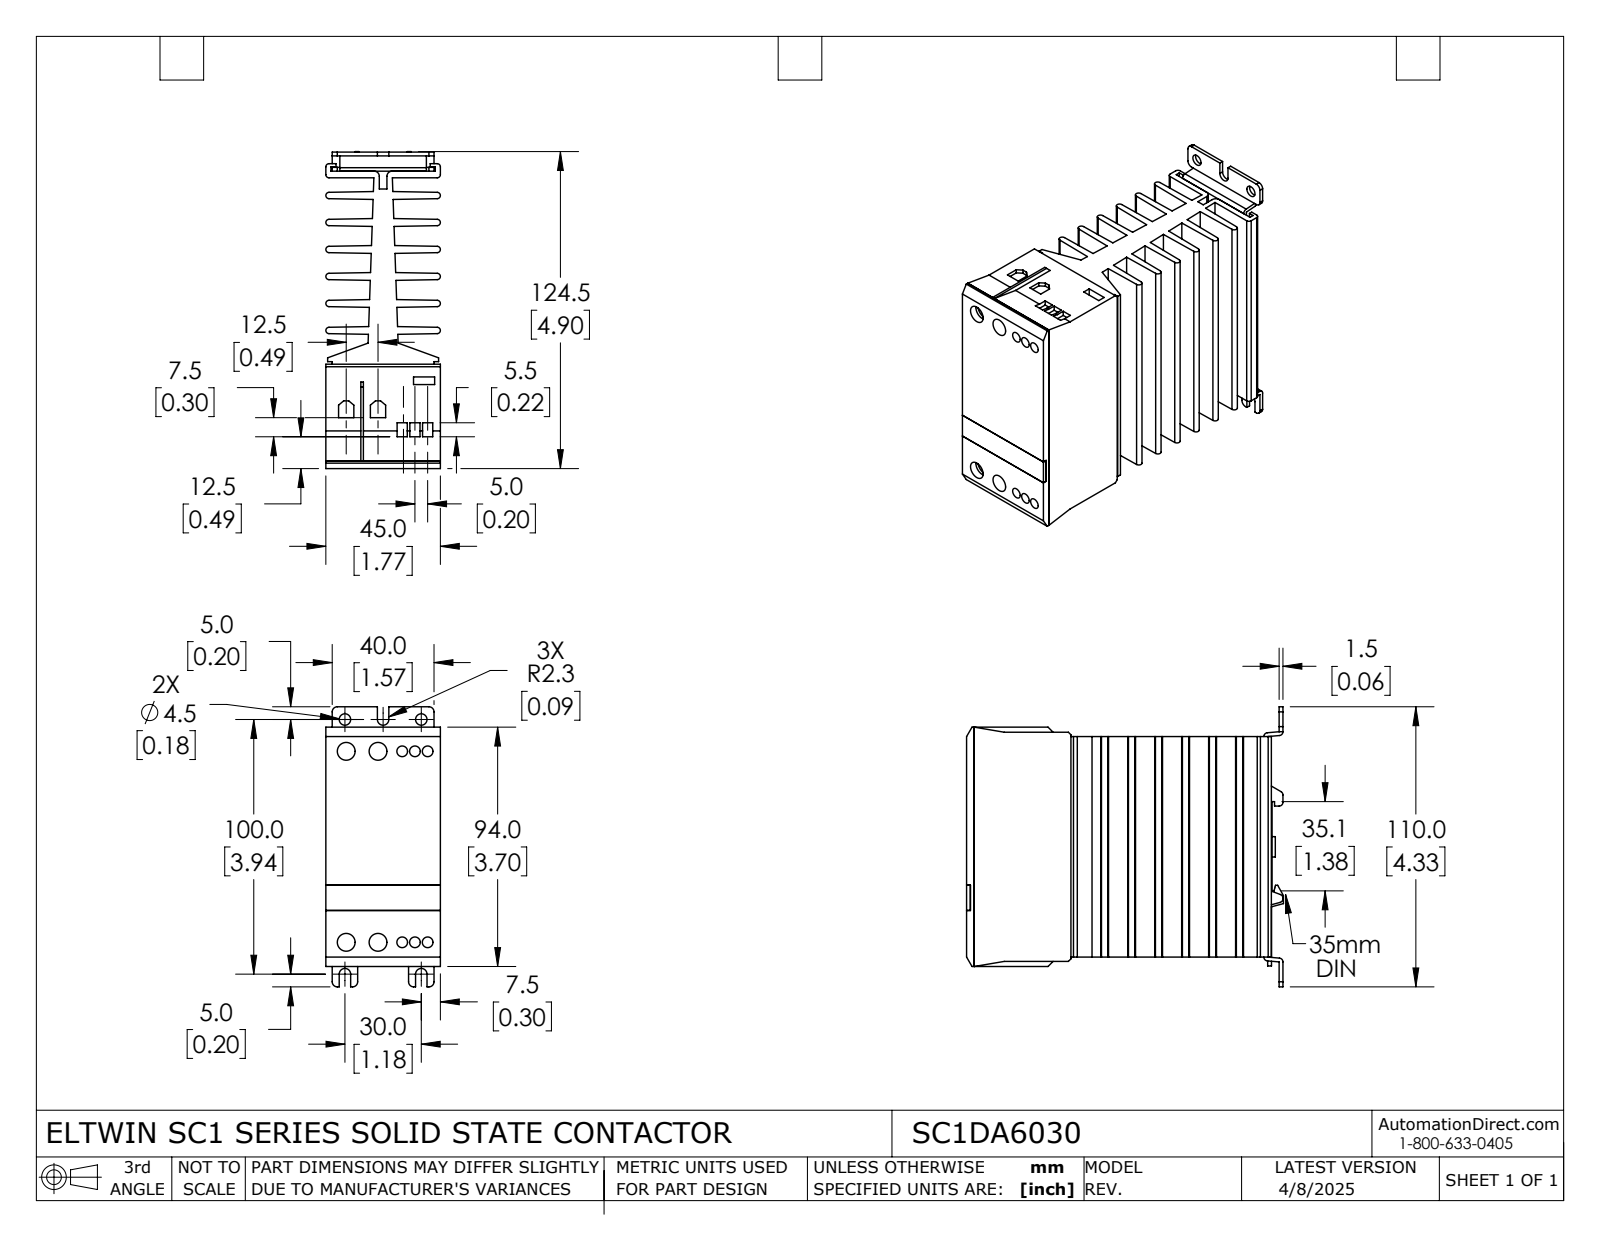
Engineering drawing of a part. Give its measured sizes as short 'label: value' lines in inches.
name: SC1DA6030
written by: SolidWorks 2021 (AUTOMOTIVE_DESIGN)
unit: in
bodies: 7 solids, 391 faces (284 planar, 107 cylindrical, 0 other)
size: 4.902 × 4.331 × 1.772
volume: 18.87 in³; area: 165.4 in²
holes: 6× ⌀0.165, 6× ⌀0.173, 4× ⌀0.276, 2× ⌀0.177, 2× ⌀0.315
bosses: 3× ⌀0.315
rounds: 18× R0.079, 16× R0.049, 10× R0.059, 4× R0.051, 3× R0.089
face distances: 0.417, 0.835, 0.127, 1.252, 0.29, 0.544, 0.707, 0.962, 1.669, 1.125
hole spacings: 2.953, 0.197, 2.959, 0.374, 0.394, 0.492, 0.502, 0.571
